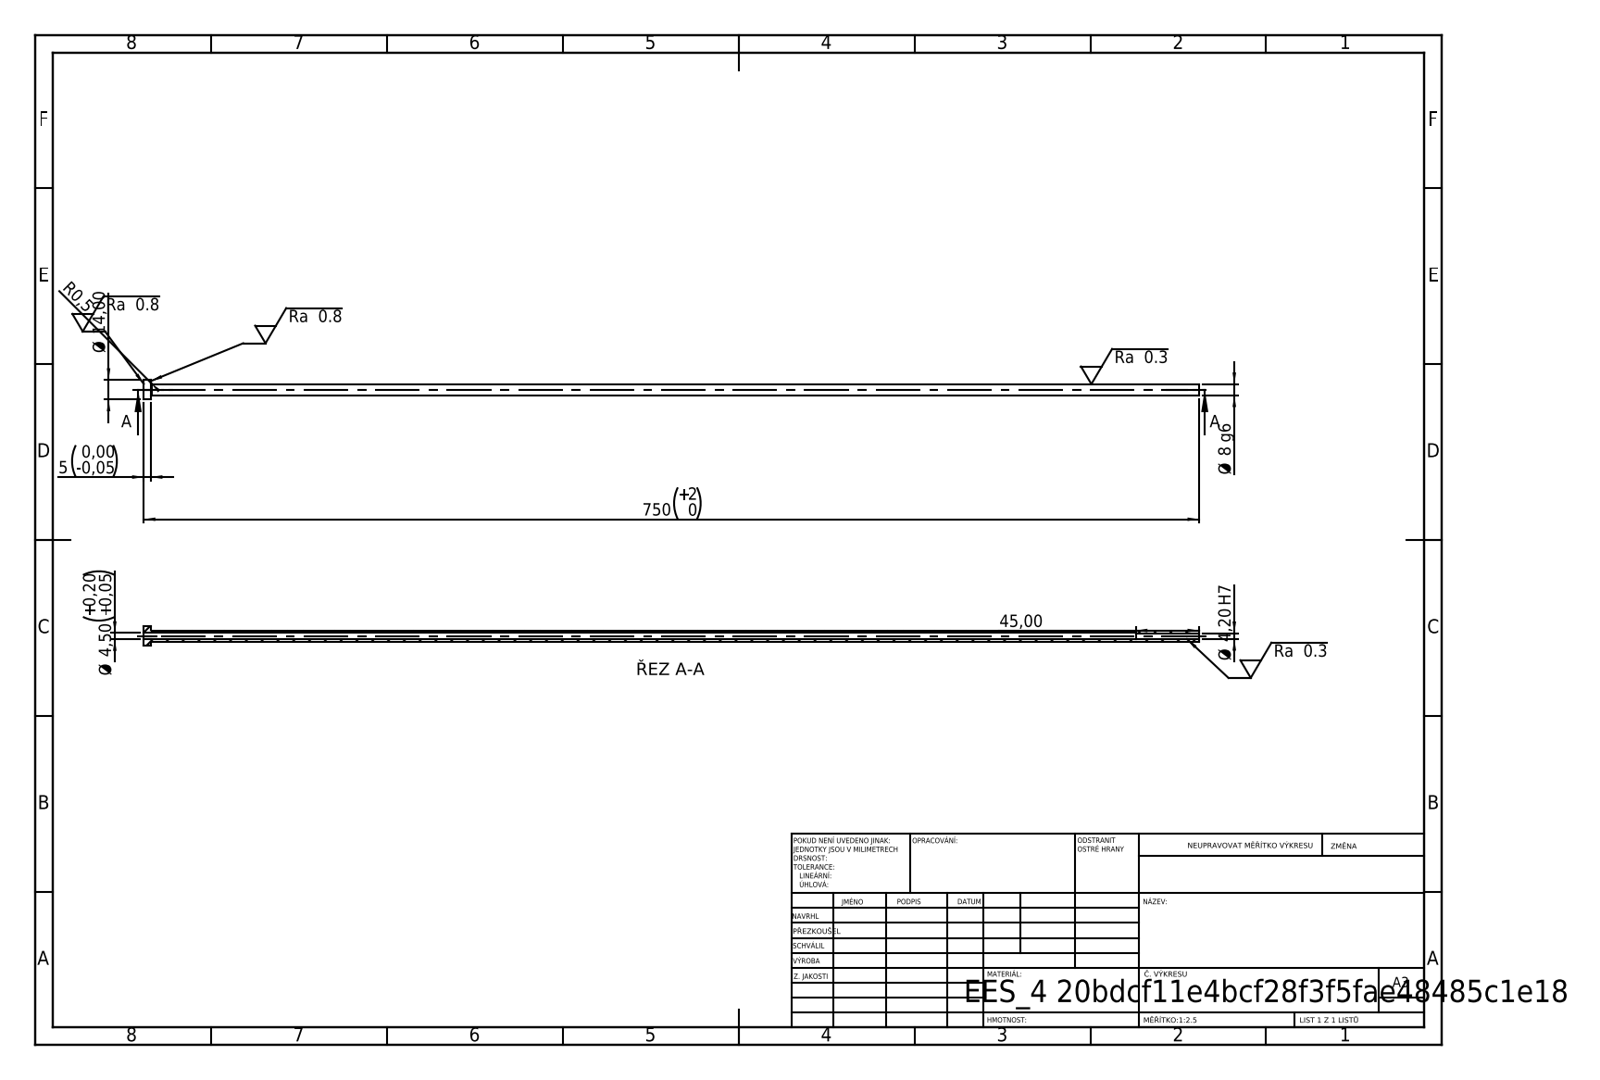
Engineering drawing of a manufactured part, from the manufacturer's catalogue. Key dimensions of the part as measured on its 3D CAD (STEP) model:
STEP written by: SolidWorks 2019 (CONFIG_CONTROL_DESIGN)
Units: millimetres
Bodies: 1 solid, 14 faces (4 planar, 8 cylindrical, 2 other)
Overall size (bounding box): 750 × 14 × 14
Volume: 26 383 mm³ · Surface area: 29 779 mm²
Round holes (diameter × count): ⌀4.2 ×1, ⌀4.5 ×1
Round bosses / shafts (diameter × count): ⌀14 ×1, ⌀8 ×1
Main face-to-face distances: 5, 750, 745, 705, 700, 45
